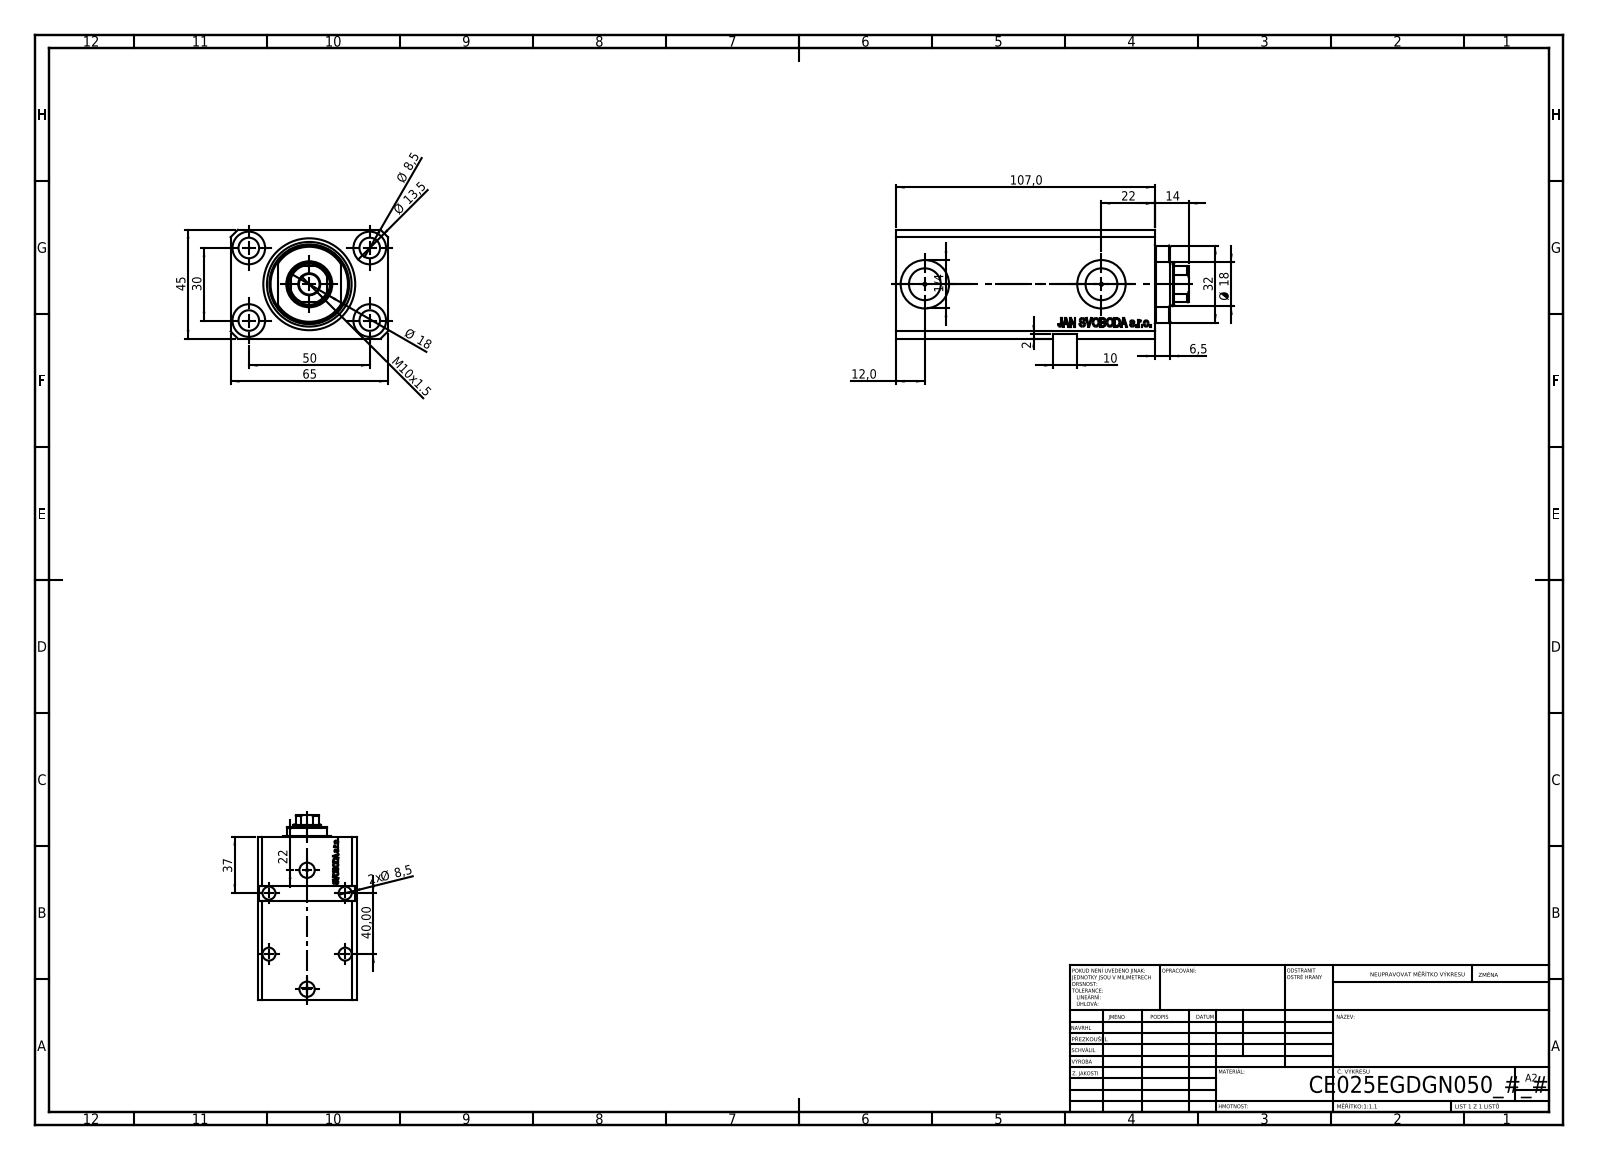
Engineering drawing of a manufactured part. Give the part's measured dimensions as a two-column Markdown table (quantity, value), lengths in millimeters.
| quantity | value |
| --- | --- |
| part name | V250CE_C_VCP; V250CE_VC_E; V250CE_E_Body |
| STEP written by | SolidWorks 2019 (CONFIG_CONTROL_DESIGN) |
| units | millimeters |
| bodies | 3 solids, 933 faces (439 planar, 116 cylindrical, 378 other) |
| overall size | 121 × 65 × 45 |
| volume | 257 937 mm³ |
| surface area | 68 062 mm² |
| round holes (diameter × count) | 8.5 × 9, 1.25 × 4, 13.5 × 4, 10 × 2, 13.16 × 2, 20 × 2, 18 × 1, 25 × 1, 38 × 1 |
| partial cylindrical surfaces (radius × count) | 8.5 × 1, 16 × 1 |
| main face-to-face distances | 45, 65, 93, 14, 107, 6.9, 86.1, 100.1, 43, 64.9 |
| hole center spacings | 29.15, 50, 30, 33.61, 33.97, 40, 58.31, 60.42 |
